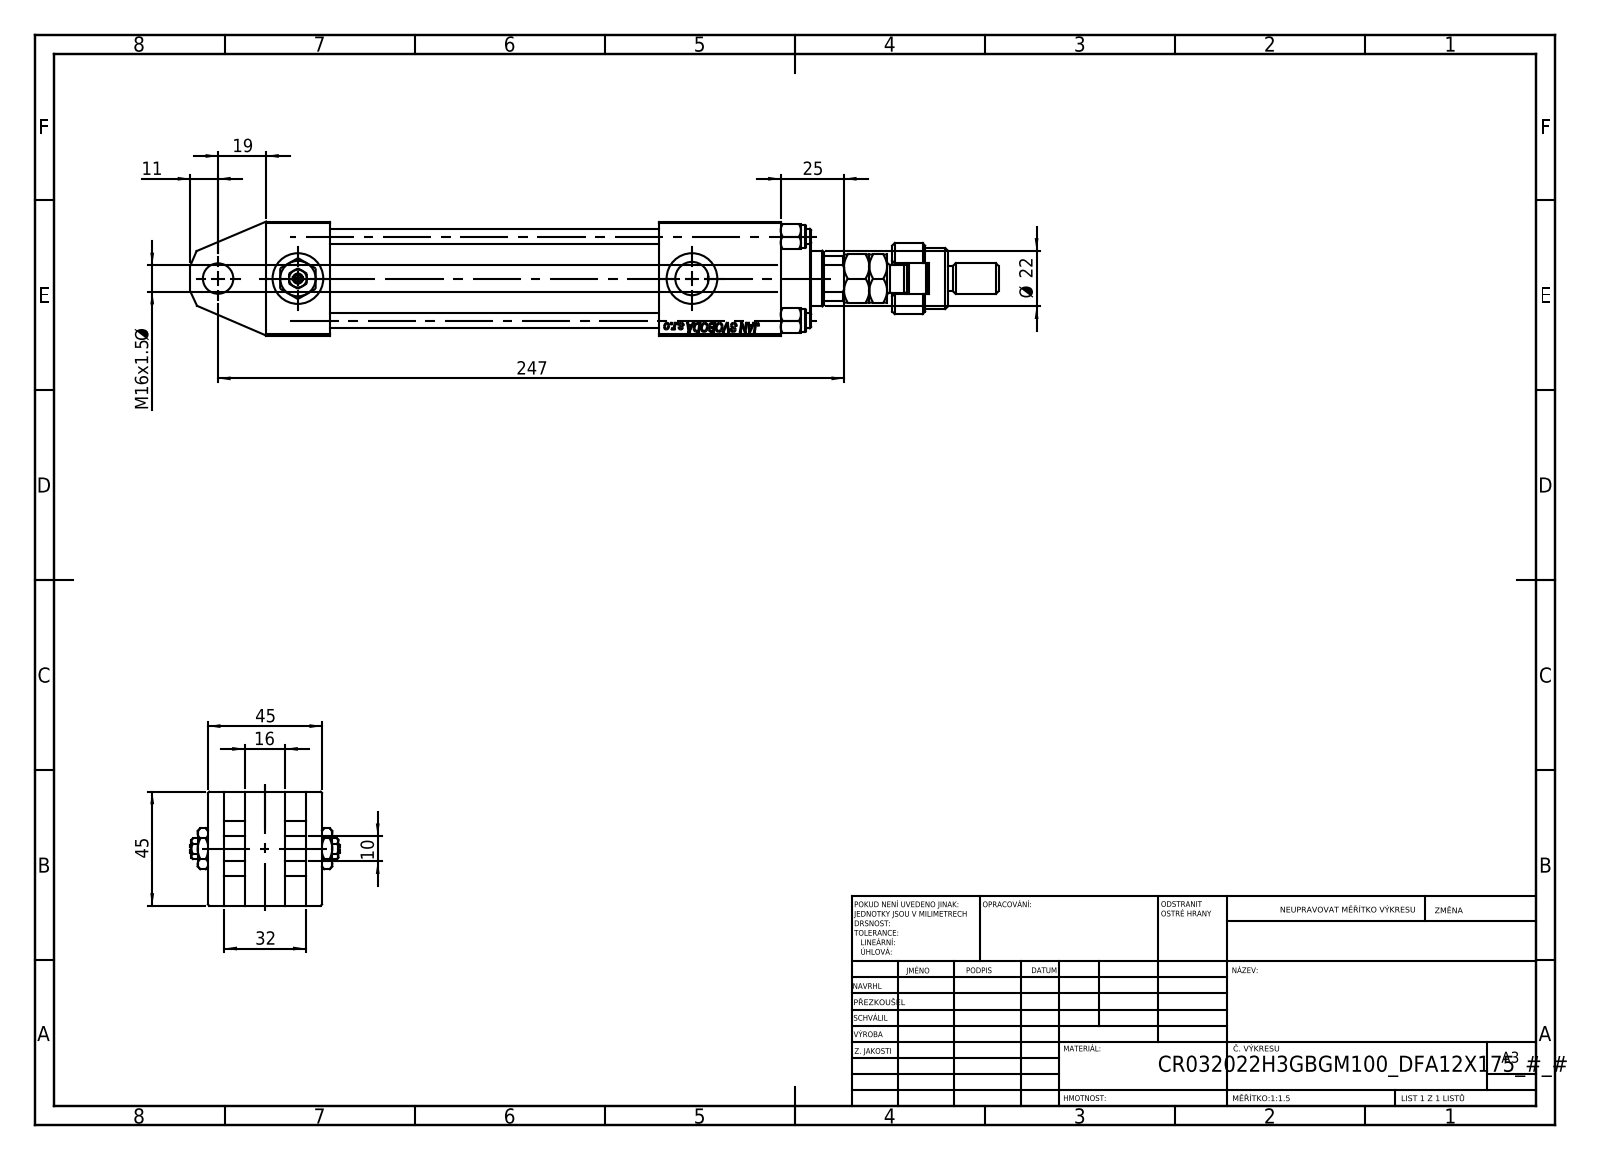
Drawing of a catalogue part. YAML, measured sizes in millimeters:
part_name: "Zatka_pro_OIL_PORT; V215CR_TYCINKA_H; NUT_M5_H; MFA (+4 more)"
step_written_by: "SolidWorks 2019 (CONFIG_CONTROL_DESIGN)"
units: millimeters
bodies: {solids: 15, faces: 1313, planar: 592, cylindrical: 107, other: 614}
overall_size: [319, 59, 45]
volume: 307010
surface_area: 116539
round_holes:
  - {diameter: 6, count: 4}
  - {diameter: 7, count: 2}
  - {diameter: 13.16, count: 2}
  - {diameter: 20, count: 2}
  - {diameter: 10.5, count: 1}
  - {diameter: 12, count: 1}
  - {diameter: 22, count: 1}
  - {diameter: 24, count: 1}
  - {diameter: 25, count: 1}
  - {diameter: 32, count: 1}
  - {diameter: 33, count: 1}
round_bosses_or_shafts:
  - {diameter: 9, count: 4}
  - {diameter: 38, count: 1}
  - {diameter: 34, count: 1}
  - {diameter: 28, count: 1}
  - {diameter: 18, count: 1}
  - {diameter: 12, count: 1}
  - {diameter: 11, count: 1}
  - {diameter: 10, count: 1}
partial_cylinders:
  - {radius: 9.75, count: 1}
  - {radius: 10.5, count: 1}
face_to_face_distances: [45, 8, 25, 14.5, 38.5, 24, 30.5, 6.5, 203, 32]
hole_center_spacings: [23.48, 33.2, 46.95, 31.5, 155.5, 187]
